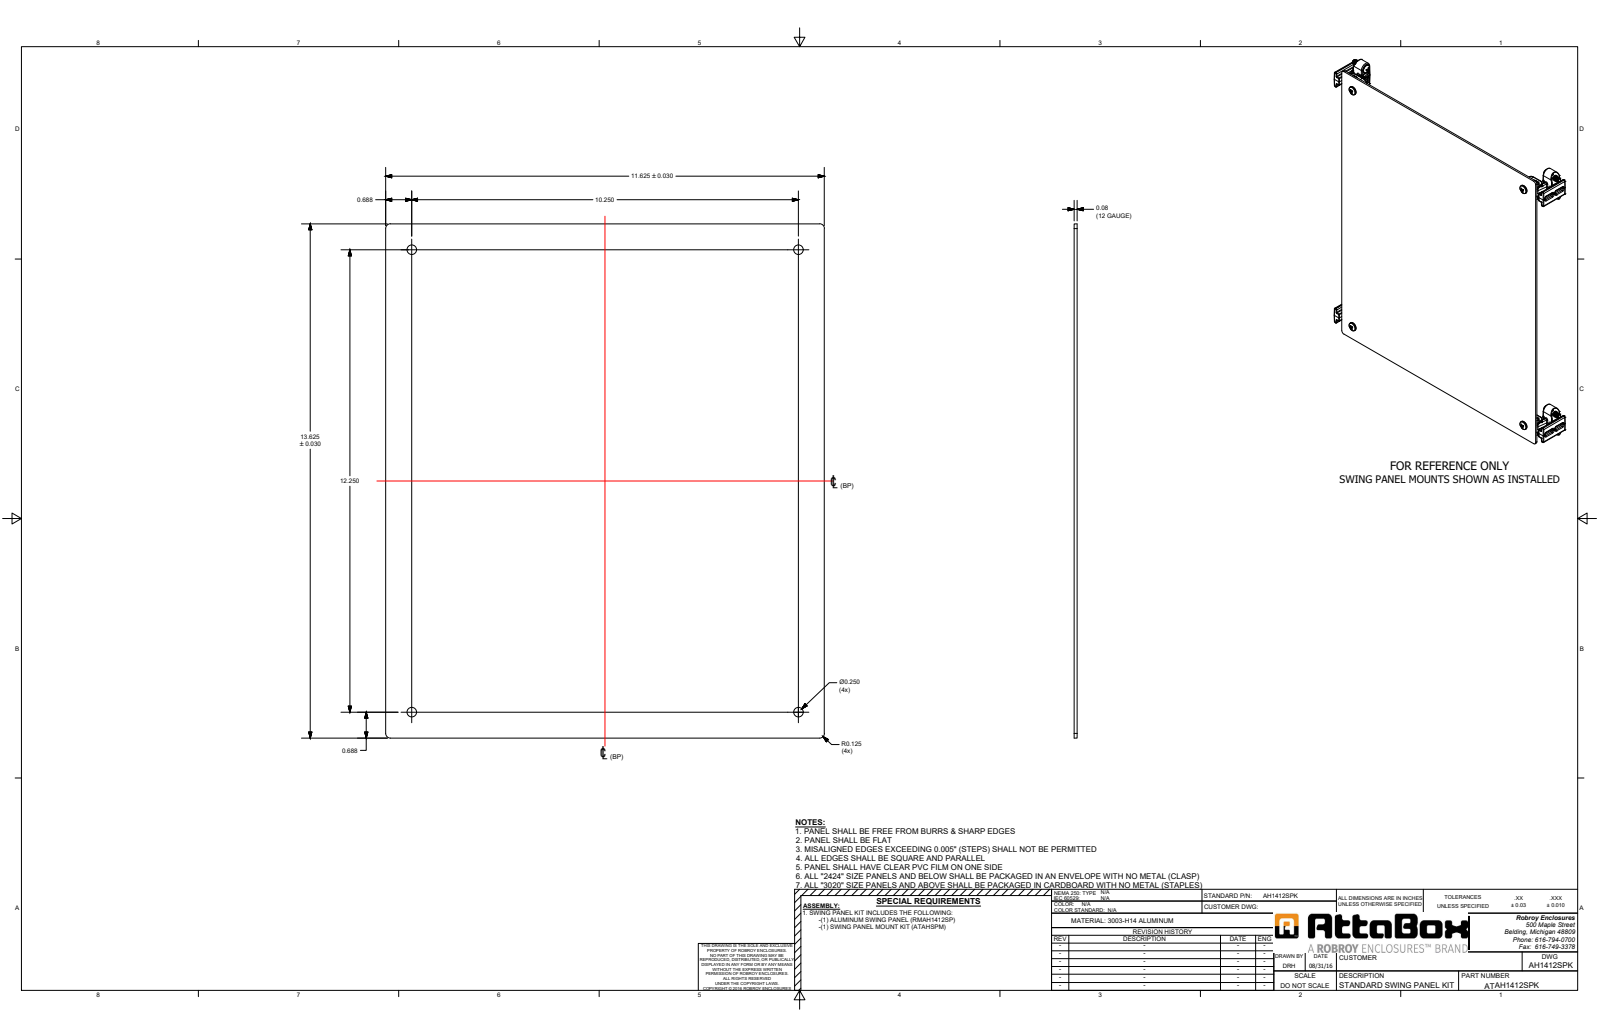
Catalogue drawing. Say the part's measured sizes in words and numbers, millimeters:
The part is named "AH1412SPK". Its 3-D file was written by "SolidWorks 2019 (AUTOMOTIVE_DESIGN)". It is 33 solids with 2010 faces: 518 planar, 736 cylindrical and 756 other. Overall it measures 346.1 by 319 by 36.8 millimeters. Its volume is 257 900 cubic millimeters and its surface area 243 900 square millimeters. Round holes: 8 of diameter 4, 8 of diameter 6.4. Round bosses or shafts: 8 of diameter 9.5, 8 of diameter 6.7, 8 of diameter 4.8. Partial cylindrical surfaces (rounded edges, fillets, slot ends): 248 of radius 0.9, 124 of radius 0.5, 54 of radius 1.7, 30 of radius 0.4, 16 of radius 1.1, 16 of radius 1.3, 14 of radius 0.6, 8 of radius 22.9. The main face-to-face distances are 2, 5.3, 311.2, 12.7, 13, 15, 319, 295.3, 7.6, 311.4. The hole center spacings are 311.2, 22.2, 260.4, 405.7, 288.9, 333.4.
